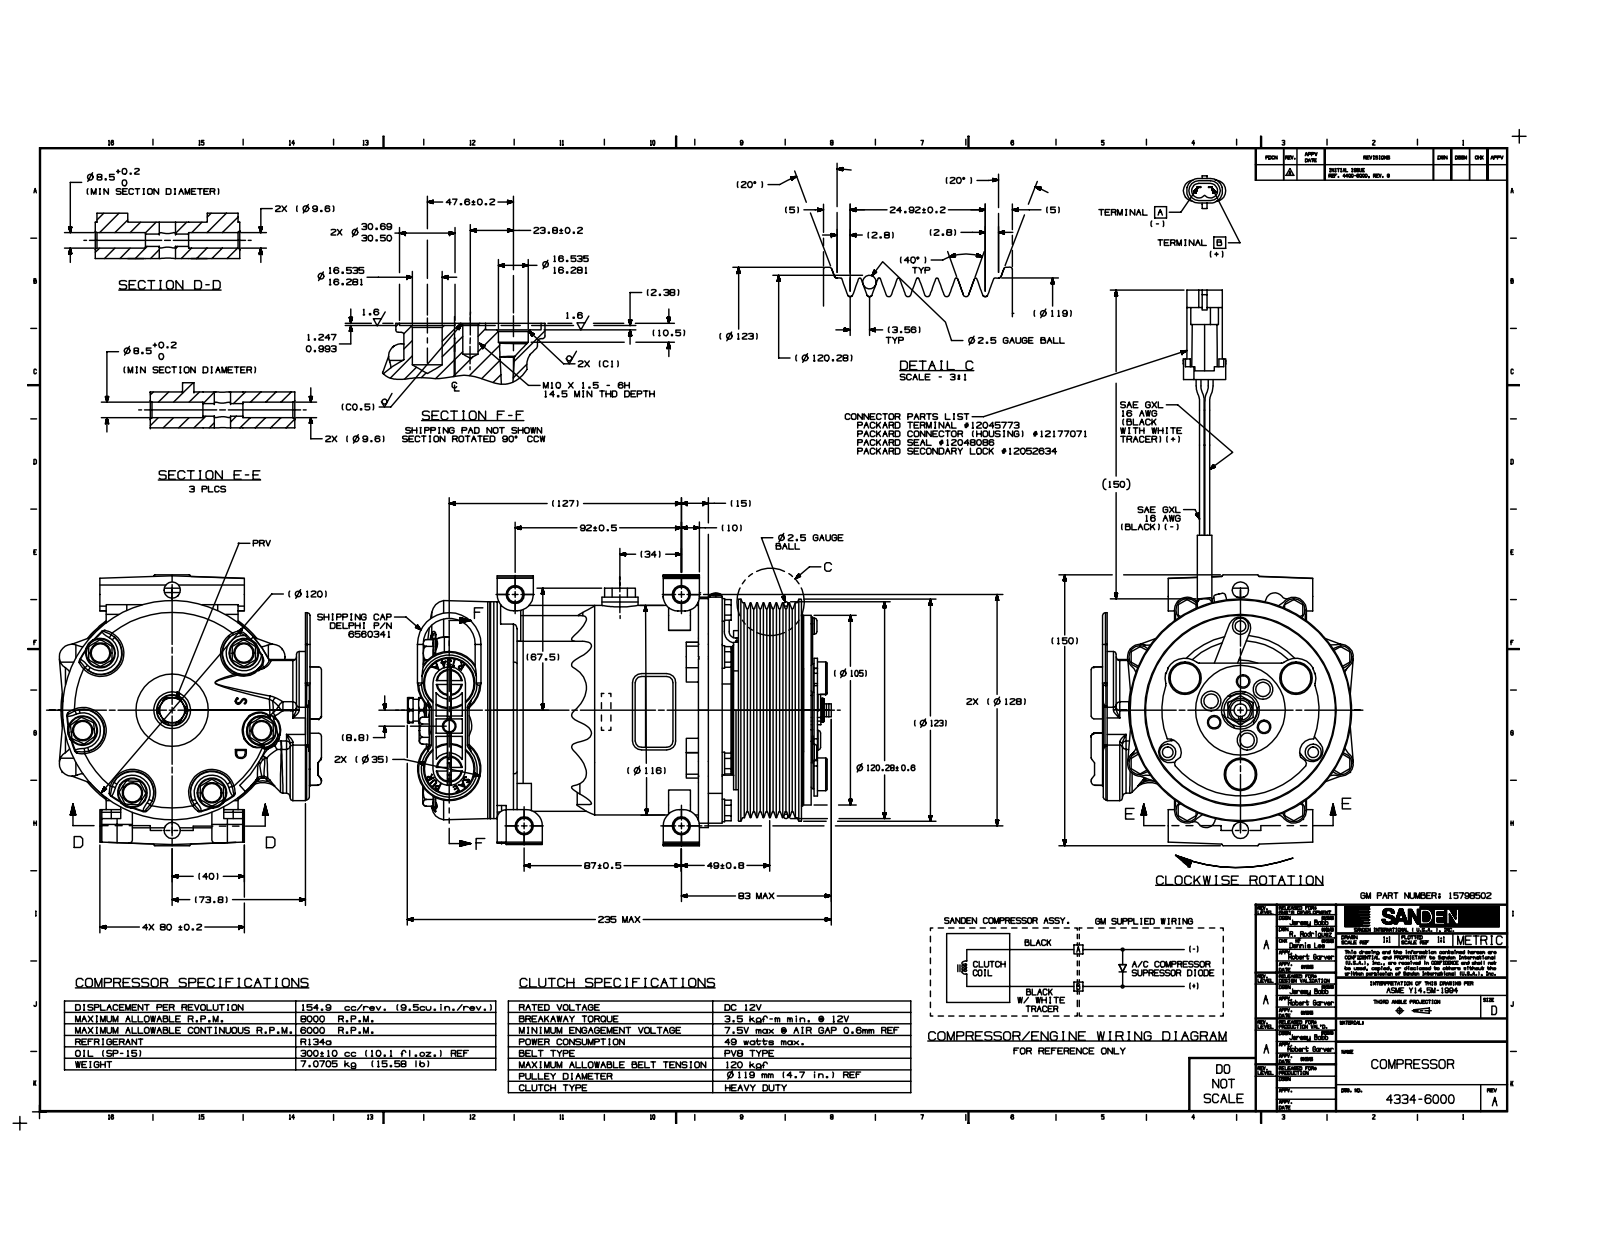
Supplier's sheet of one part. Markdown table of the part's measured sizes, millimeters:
| quantity | value |
| --- | --- |
| part name | SANDEN_4334_REV_A_COMPR_AC |
| STEP written by | SolidWorks 2010 (CONFIG_CONTROL_DESIGN) |
| units | millimeters |
| bodies | 2 solids, 2779 faces (636 planar, 686 cylindrical, 1457 other) |
| overall size | 307.41 × 232.96 × 145.1 |
| volume | 2 344 000 mm³ |
| surface area | 224 158 mm² |
| round holes (diameter × count) | 8 × 8, 8.75 × 8, 5.1 × 6, 7.5 × 6, 11.29 × 6, 8.5 × 5, 15 × 4, 4.1 × 3, 6.35 × 3, 13 × 3, 8.8 × 2, 16.54 × 2 |
| round bosses / shafts (diameter × count) | 12.5 × 8, 5 × 6, 18 × 3, 16 × 3, 11 × 3, 9 × 3, 7.4 × 3, 4 × 3 |
| partial cylindrical surfaces (radius × count) | 0.5 × 36, 3 × 26, 7 × 25, 1.5 × 24, 2 × 22, 2.5 × 21, 5 × 21, 0.1 × 18 |
| main face-to-face distances | 4.2, 35.96, 40.76, 4.8, 0.6, 36.56, 2, 1.5, 6.3, 3.5 |
| hole center spacings | 62.85, 88.89, 42.09, 16, 31.48, 36.77, 59, 66.7 |
